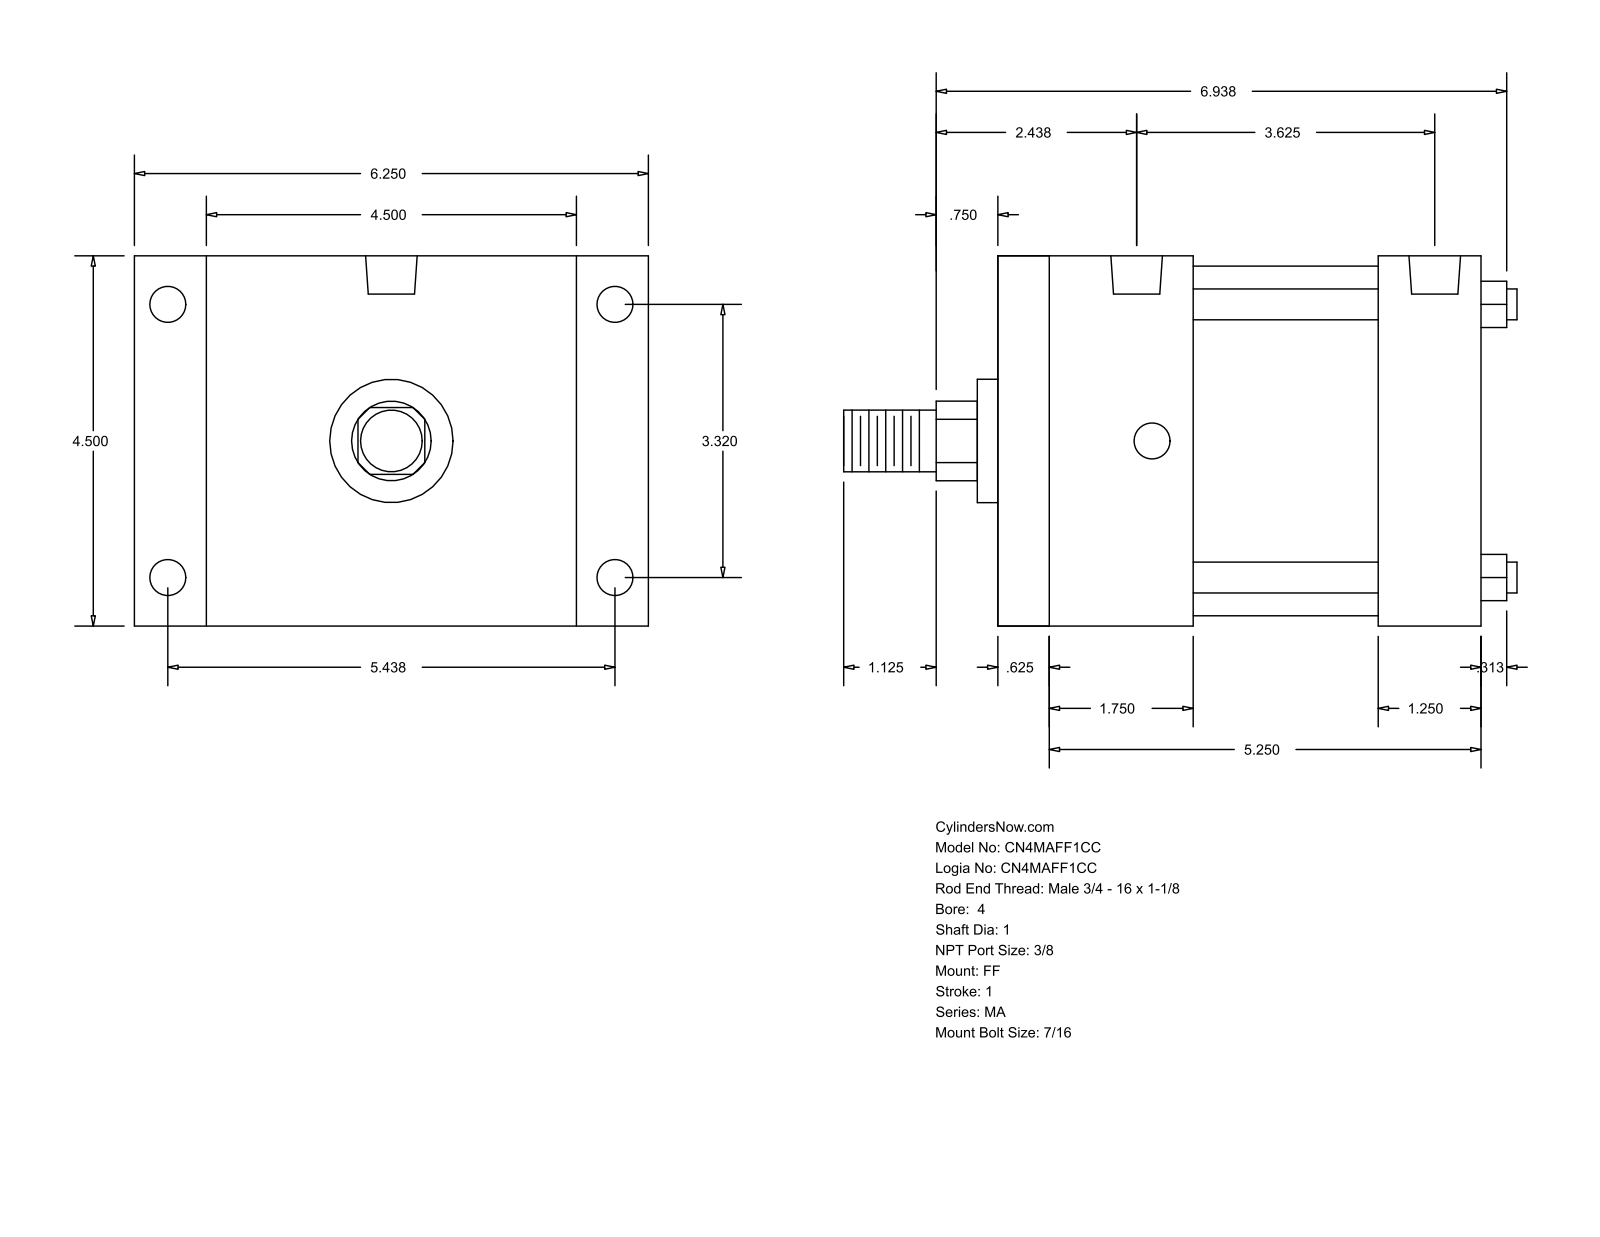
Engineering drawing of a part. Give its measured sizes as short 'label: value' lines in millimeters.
name: MA_FF__0400_1
written by: GSSL Pune (CONFIG_CONTROL_DESIGN)
unit: mm
bodies: 0 solids, 92 faces (64 planar, 28 cylindrical, 0 other)
size: 207.96 × 158.75 × 114.3
holes: 8× ⌀11.11, 2× ⌀15.93
bosses: 4× ⌀9.53, 1× ⌀107.95, 1× ⌀38.1, 1× ⌀25.4, 1× ⌀19.05
rounds: 1× R12.29
face distances: 114.3, 149.23, 15.87, 133.36, 136.53, 22.23, 117.48, 101.61, 31.75, 60.33
hole spacings: 82.55, 84.32, 138.12, 161.82, 4.76, 4.77, 87.31, 87.32
